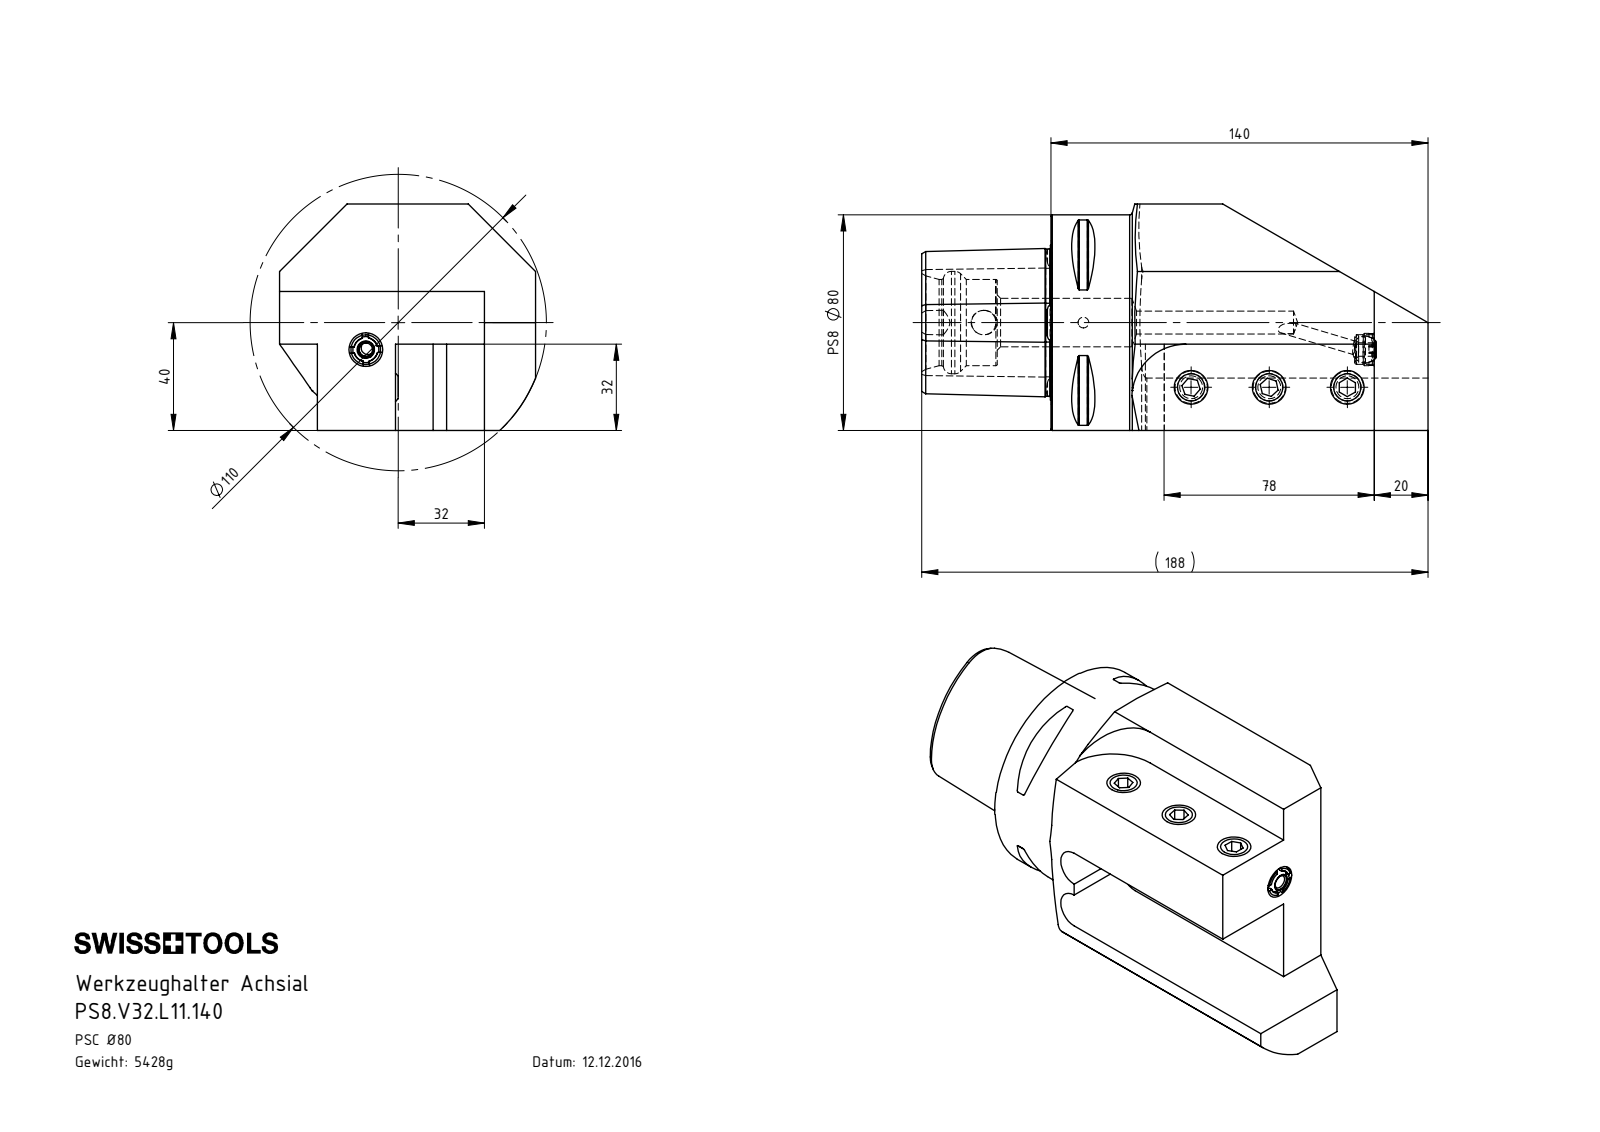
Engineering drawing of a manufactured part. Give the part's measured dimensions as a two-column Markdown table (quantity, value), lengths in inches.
| quantity | value |
| --- | --- |
| part name | PS8-V32.L11.140; PS8-V32.L11.140_A; DIN 3771 - 8x1.5; KU1-U12.003.010_A (+3 more) |
| STEP written by | SolidWorks 2017 (AUTOMOTIVE_DESIGN) |
| units | inches |
| bodies | 7 solids, 270 faces (79 planar, 58 cylindrical, 133 other) |
| overall size | 7.402 × 3.74 × 3.307 |
| volume | 42.2 in³ |
| surface area | 122 in² |
| round holes (diameter × count) | 0.402 × 3, 0.197 × 2, 0.157 × 1, 0.335 × 1, 0.358 × 1, 0.394 × 1, 0.433 × 1, 0.709 × 1, 1.26 × 1, 1.496 × 1 |
| round bosses / shafts (diameter × count) | 0.472 × 4, 3.15 × 1 |
| partial cylindrical surfaces (radius × count) | 0.02 × 8, 0.276 × 2, 0.173 × 1, 0.236 × 1, 0.472 × 1, 0.787 × 1, 2.165 × 1 |
| main face-to-face distances | 2.047, 1.26, 0.748, 2.441, 3.189, 2.992, 3.74, 0.551, 1.299, 1.142 |
| hole center spacings | 1.142, 0.615, 1.457, 1.837, 2.283, 2.876, 3.175, 3.972 |
